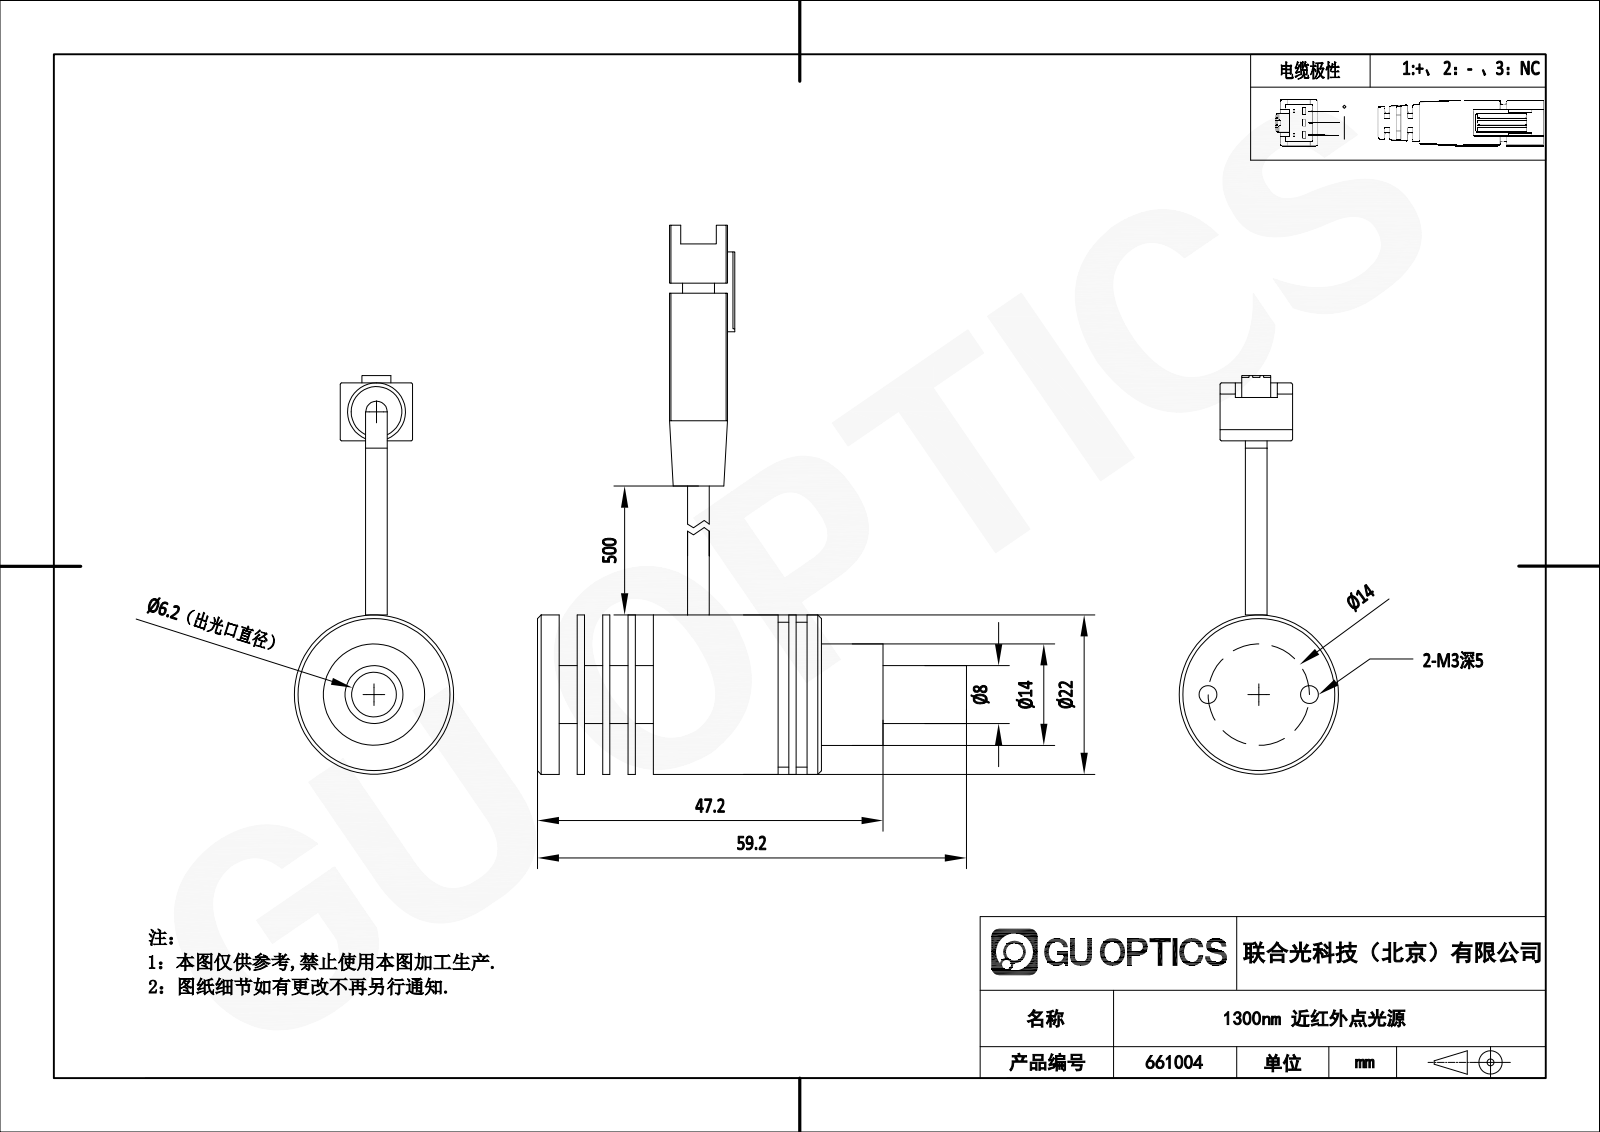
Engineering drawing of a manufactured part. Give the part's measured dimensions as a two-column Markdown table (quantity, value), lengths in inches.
| quantity | value |
| --- | --- |
| part name | 661002 |
| STEP written by | SolidWorks 2020 (CONFIG_CONTROL_DESIGN) |
| units | inches |
| bodies | 3 solids, 104 faces (69 planar, 29 cylindrical, 6 other) |
| overall size | 4.448 × 2.165 × 0.866 |
| volume | 0.978 in³ |
| surface area | 13.51 in² |
| round holes (diameter × count) | 0.098 × 2, 0.244 × 1 |
| round bosses / shafts (diameter × count) | 0.118 × 2, 0.866 × 1, 0.787 × 1, 0.551 × 1, 0.315 × 1 |
| partial cylindrical surfaces (radius × count) | 0.008 × 4 |
| main face-to-face distances | 0.138, 0.098, 0.276, 0.236, 0.039, 0.177, 0.413, 0.374, 0.394, 0.315 |
| hole center spacings | 0.276, 0.551 |
